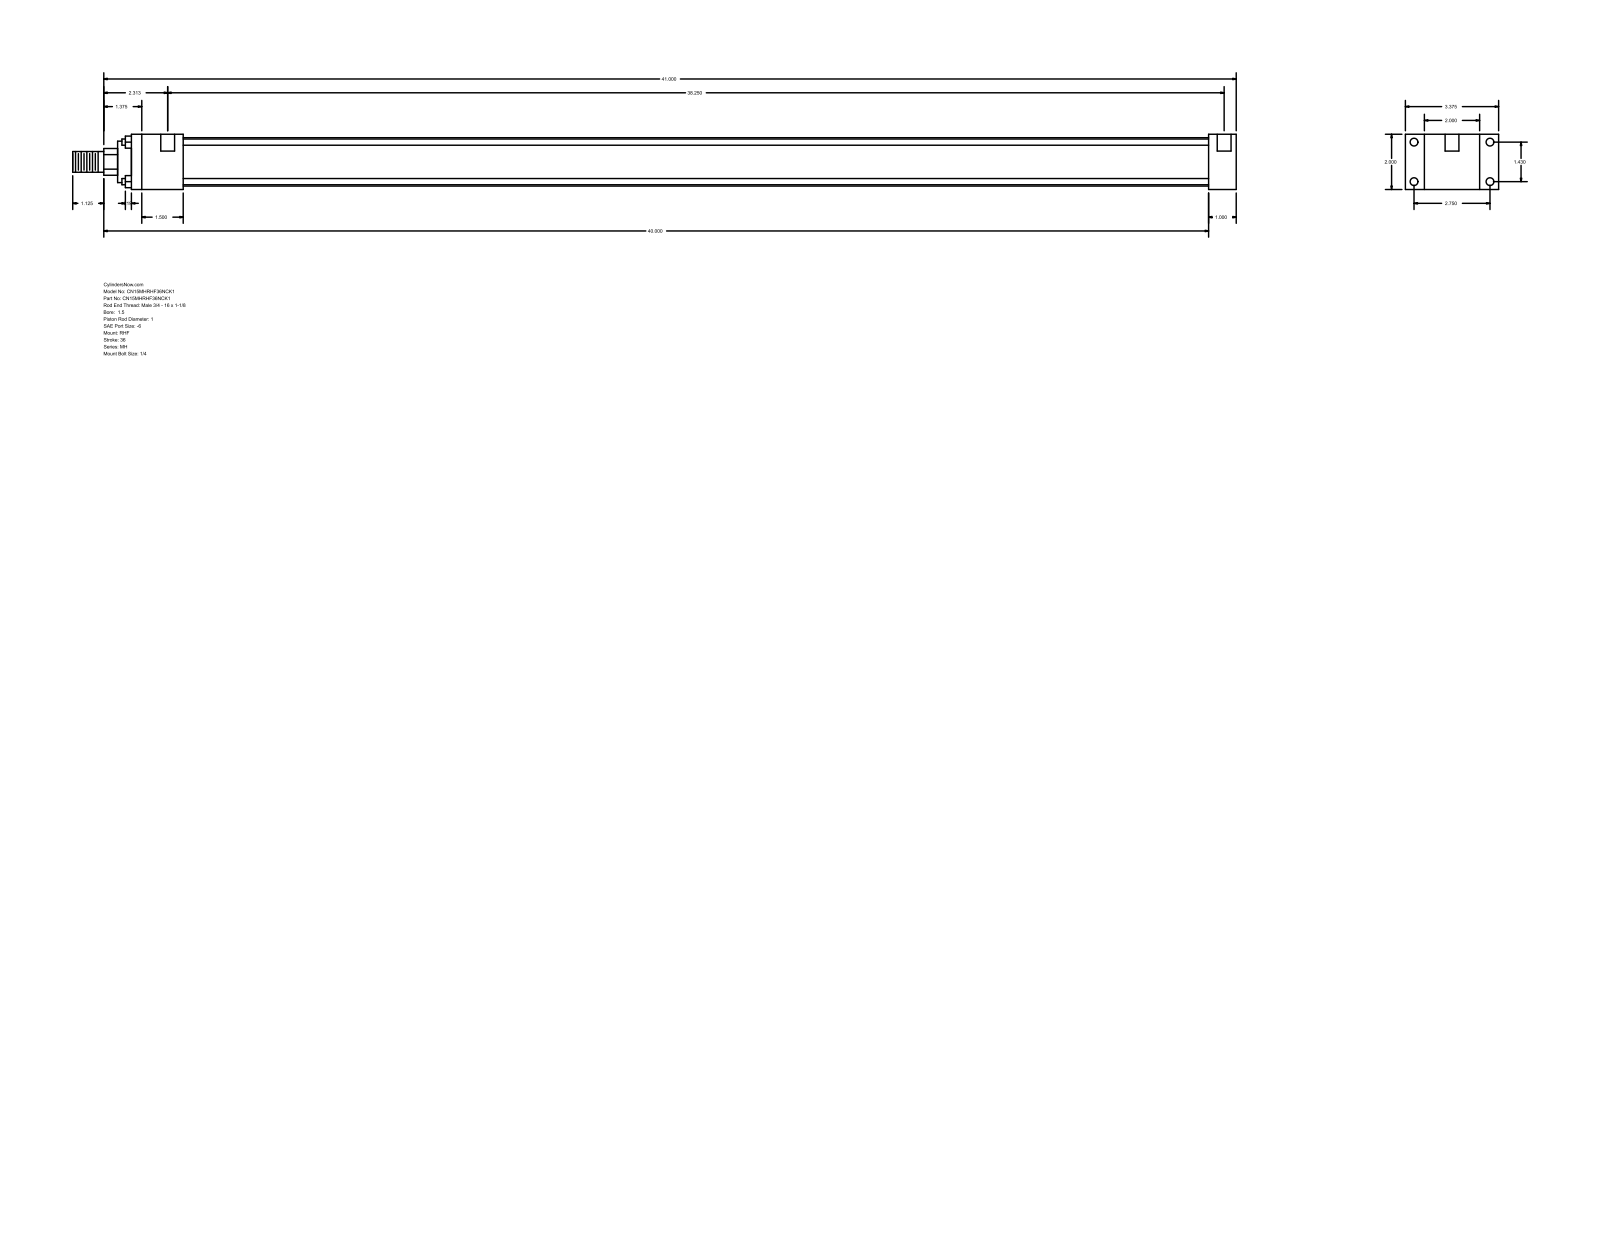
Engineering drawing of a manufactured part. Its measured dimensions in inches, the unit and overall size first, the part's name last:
Units: inches
Overall size (bounding box): 42.125 × 3.375 × 2
Round holes (diameter × count): ⌀0.219 ×4, ⌀0.281 ×4, ⌀0.5 ×2
Round bosses / shafts (diameter × count): ⌀0.225 ×4, ⌀1.75 ×1, ⌀1.5 ×1, ⌀1 ×1, ⌀0.75 ×1
Partial cylindrical surfaces — rounded edges, fillets, slot ends (radius × count): R0.484 ×1
Main face-to-face distances: 2, 1, 0.687, 2.687, 3.375, 40, 39, 1.875, 37.125, 38.125
Hole centre spacings: 1.43, 2.75, 3.099, 38.375, 0.125, 38.25
Bodies: 0 solids, 88 faces (60 planar, 28 cylindrical, 0 other)
Part name (STEP PRODUCT): MH_RHF__0150_1
STEP written by: GSSL Pune (CONFIG_CONTROL_DESIGN)
